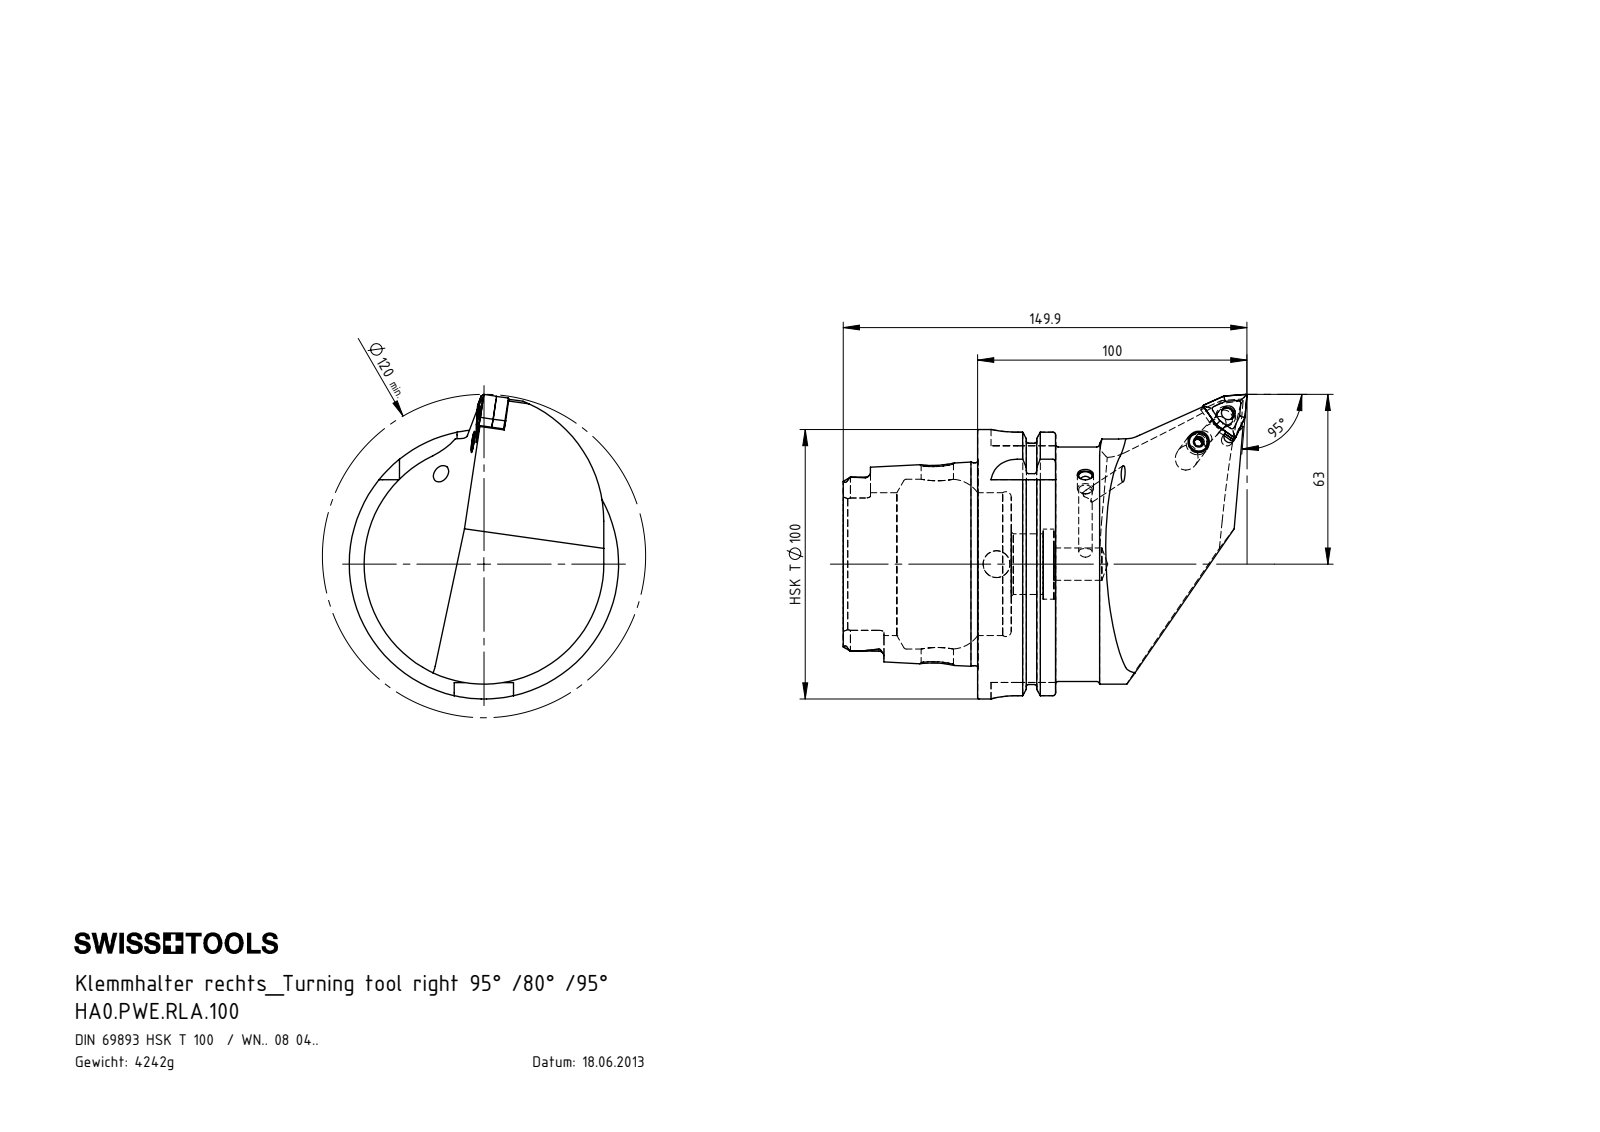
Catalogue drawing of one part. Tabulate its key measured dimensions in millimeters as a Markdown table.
| quantity | value |
| --- | --- |
| part name | WNMG080404; WDF-ER3.101.000_A; HA0-PWE.RLA.100_A; WCD-ER4.101.017_A (+4 more) |
| STEP written by | SolidWorks 2012 (CONFIG_CONTROL_DESIGN) |
| units | millimeters |
| bodies | 8 solids, 397 faces (127 planar, 107 cylindrical, 163 other) |
| overall size | 149.9 × 113 × 100 |
| volume | 543 226 mm³ |
| surface area | 71 028 mm² |
| round holes (diameter × count) | 5 × 2, 12 × 2, 5.16 × 1, 6.7 × 1, 7 × 1, 7.8 × 1, 8.4 × 1, 10 × 1, 22.5 × 1, 26 × 1, 53 × 1, 63 × 1 |
| round bosses / shafts (diameter × count) | 100 × 1, 91.95 × 1, 87 × 1, 75.26 × 1, 8 × 1, 7.9 × 1, 6.4 × 1, 6 × 1 |
| partial cylindrical surfaces (radius × count) | 1.9 × 6, 2.5 × 4, 4.88 × 4, 10 × 4, 0.4 × 3, 1 × 3, 3.2 × 2, 2.1 × 1 |
| main face-to-face distances | 12.45, 28.95, 16.5, 49.9, 62.35, 78.85, 87.8, 78.2, 28.3, 15.85 |
| hole center spacings | 15.61 |
